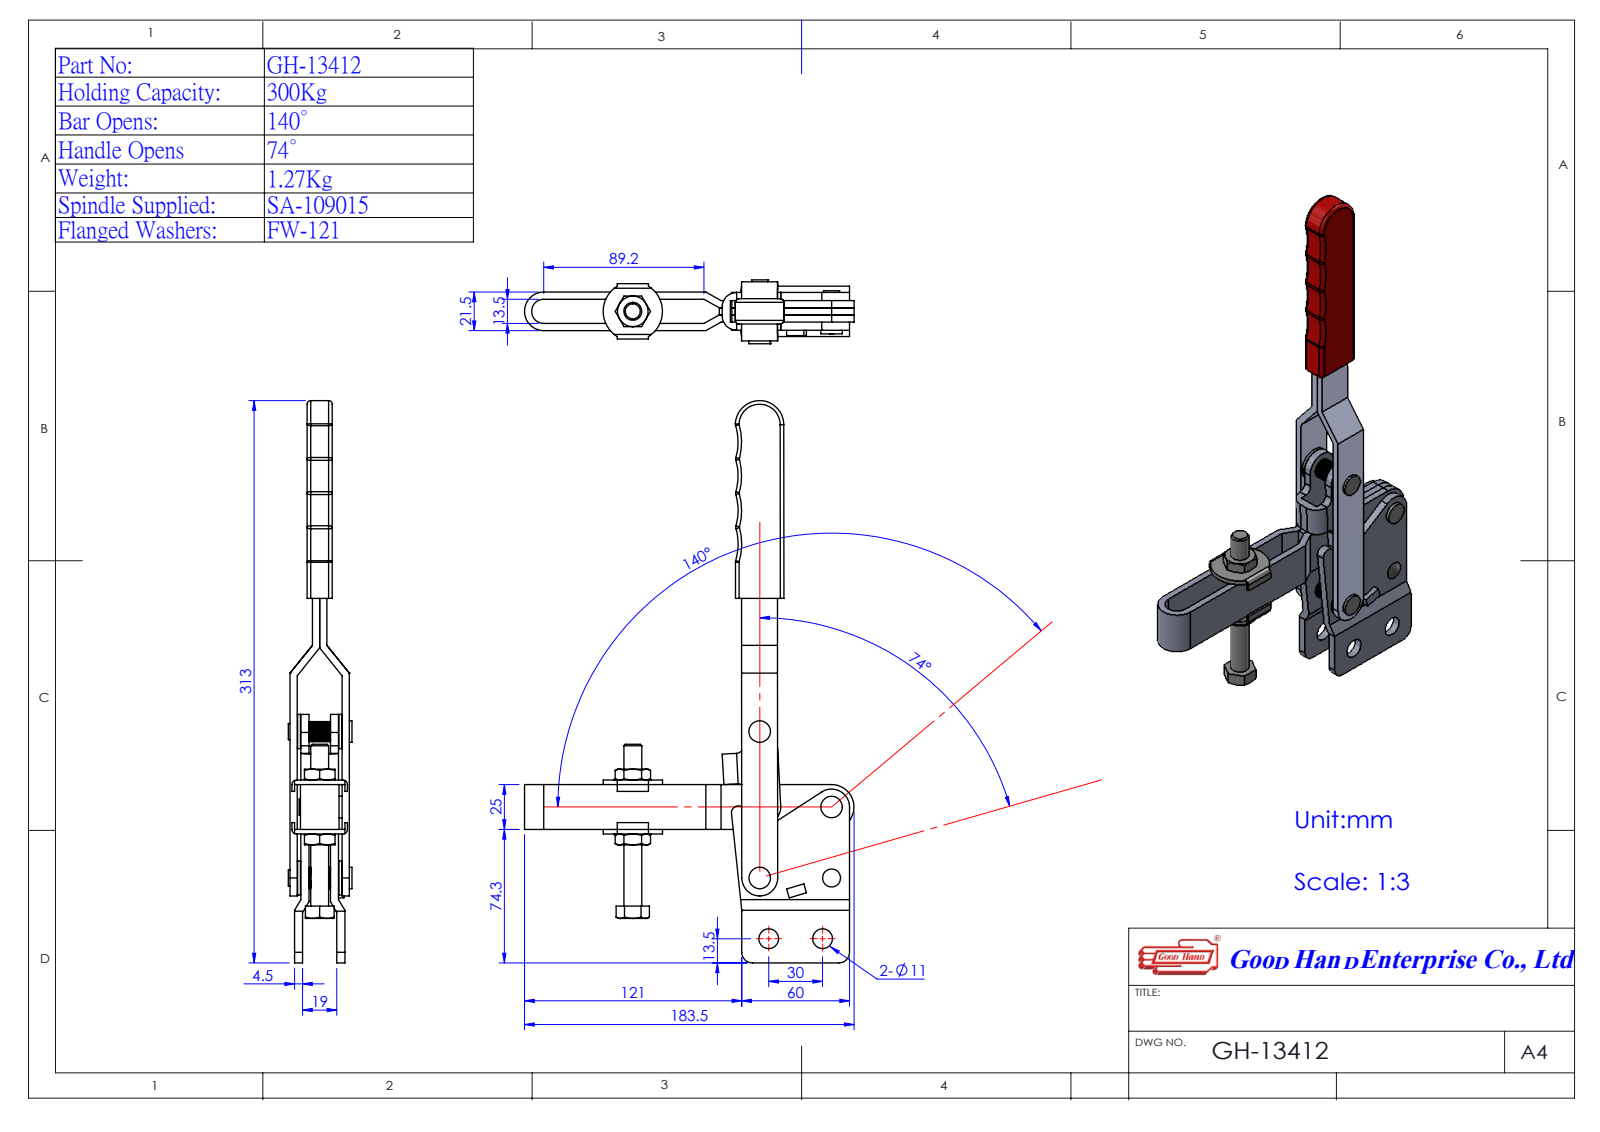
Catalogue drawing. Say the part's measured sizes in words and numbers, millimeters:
The part is named "Group5^GH-13412(簡化)-1; Group4^GH-13412(簡化)-1; Group1^GH-13412(簡化)-1; 11441208-1^GH-13412(簡化)-1 (+2 more)". Its 3-D file was written by "SolidWorks 2016 (AUTOMOTIVE_DESIGN)". It is 5 solids with 306 faces: 137 planar, 113 cylindrical and 56 other. Overall it measures 311.3 by 183.5 by 35.5 millimeters. Its volume is 188 131 cubic millimeters and its surface area 85 546 square millimeters. Round holes: 4 of diameter 6, 2 of diameter 11. Round bosses or shafts: 4 of diameter 12, 4 of diameter 9, 2 of diameter 19, 1 of diameter 10, 1 of diameter 4. Partial cylindrical surfaces (rounded edges, fillets, slot ends): 6 of radius 2, 5 of radius 3, 4 of radius 2.54, 4 of radius 32, 2 of radius 4, 2 of radius 6, 2 of radius 8, 2 of radius 10. The main face-to-face distances are 16.5, 4.5, 3.5, 4, 17.5, 3.75, 23.25, 5.75, 7, 1. The hole center spacings are 30, 34.17, 37.8, 39.56, 42.06, 48.66, 56.22, 58.03.
